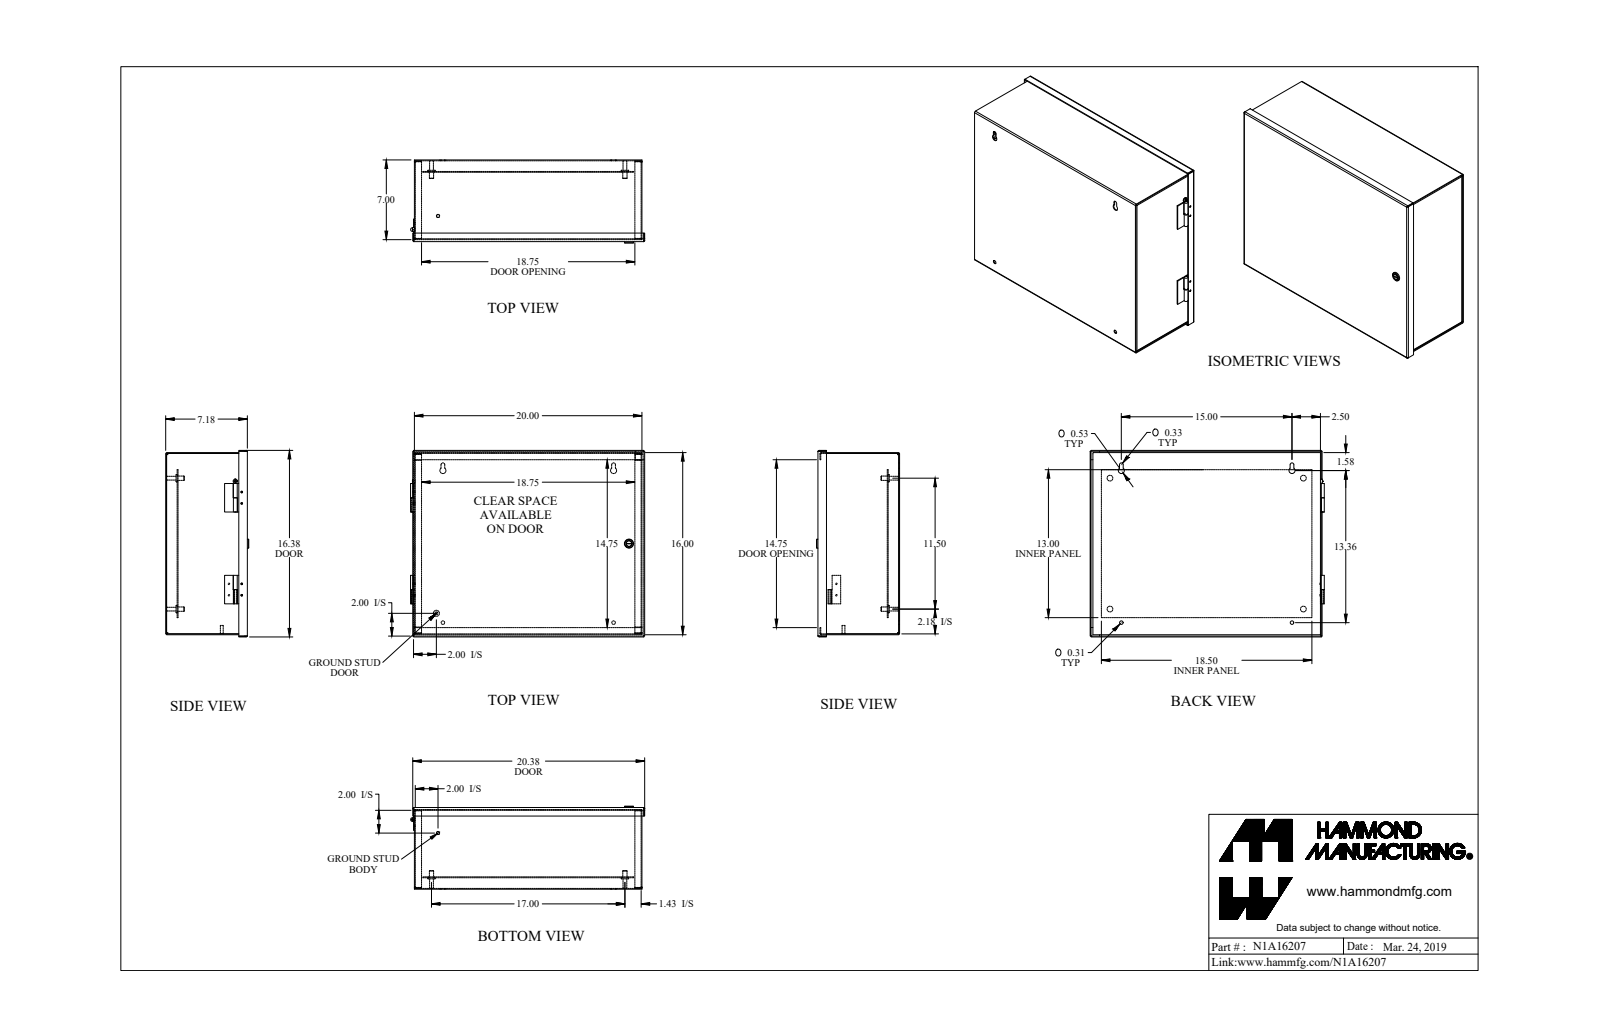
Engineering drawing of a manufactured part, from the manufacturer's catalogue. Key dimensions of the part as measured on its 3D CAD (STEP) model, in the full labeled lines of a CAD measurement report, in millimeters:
Part name (STEP PRODUCT): N1A16207
STEP written by: SolidWorks 2018 (AUTOMOTIVE_DESIGN)
Units: millimetres
Bodies: 23 solids, 529 faces (295 planar, 184 cylindrical, 50 other)
Overall size (bounding box): 522.6 × 416.2 × 185.4
Volume: 1 814 000 mm³ · Surface area: 1 988 000 mm²
Round holes (diameter × count): ⌀3.6 ×8, ⌀12.7 ×4, ⌀7.8 ×2, ⌀7.9 ×2, ⌀11.3 ×2, ⌀4.3 ×1, ⌀4.7 ×1, ⌀13.1 ×1
Round bosses / shafts (diameter × count): ⌀3.3 ×8, ⌀9.5 ×5, ⌀16.5 ×4, ⌀8.4 ×4, ⌀25.4 ×2, ⌀6.4 ×2, ⌀20 ×1, ⌀13.6 ×1
Partial cylindrical surfaces — rounded edges, fillets, slot ends (radius × count): R0.9 ×16, R2.7 ×16, R1.5 ×2, R3.9 ×2, R4.2 ×2, R6.8 ×2, R0.8 ×1, R3.2 ×1
Main face-to-face distances: 1.8, 180.5, 25.6, 154.8, 178.6, 182.3, 404.6, 27.5, 153, 23.8
Hole centre spacings: 25.4, 28.4, 28, 39.4, 51.6, 146.3, 204.8, 204.8
